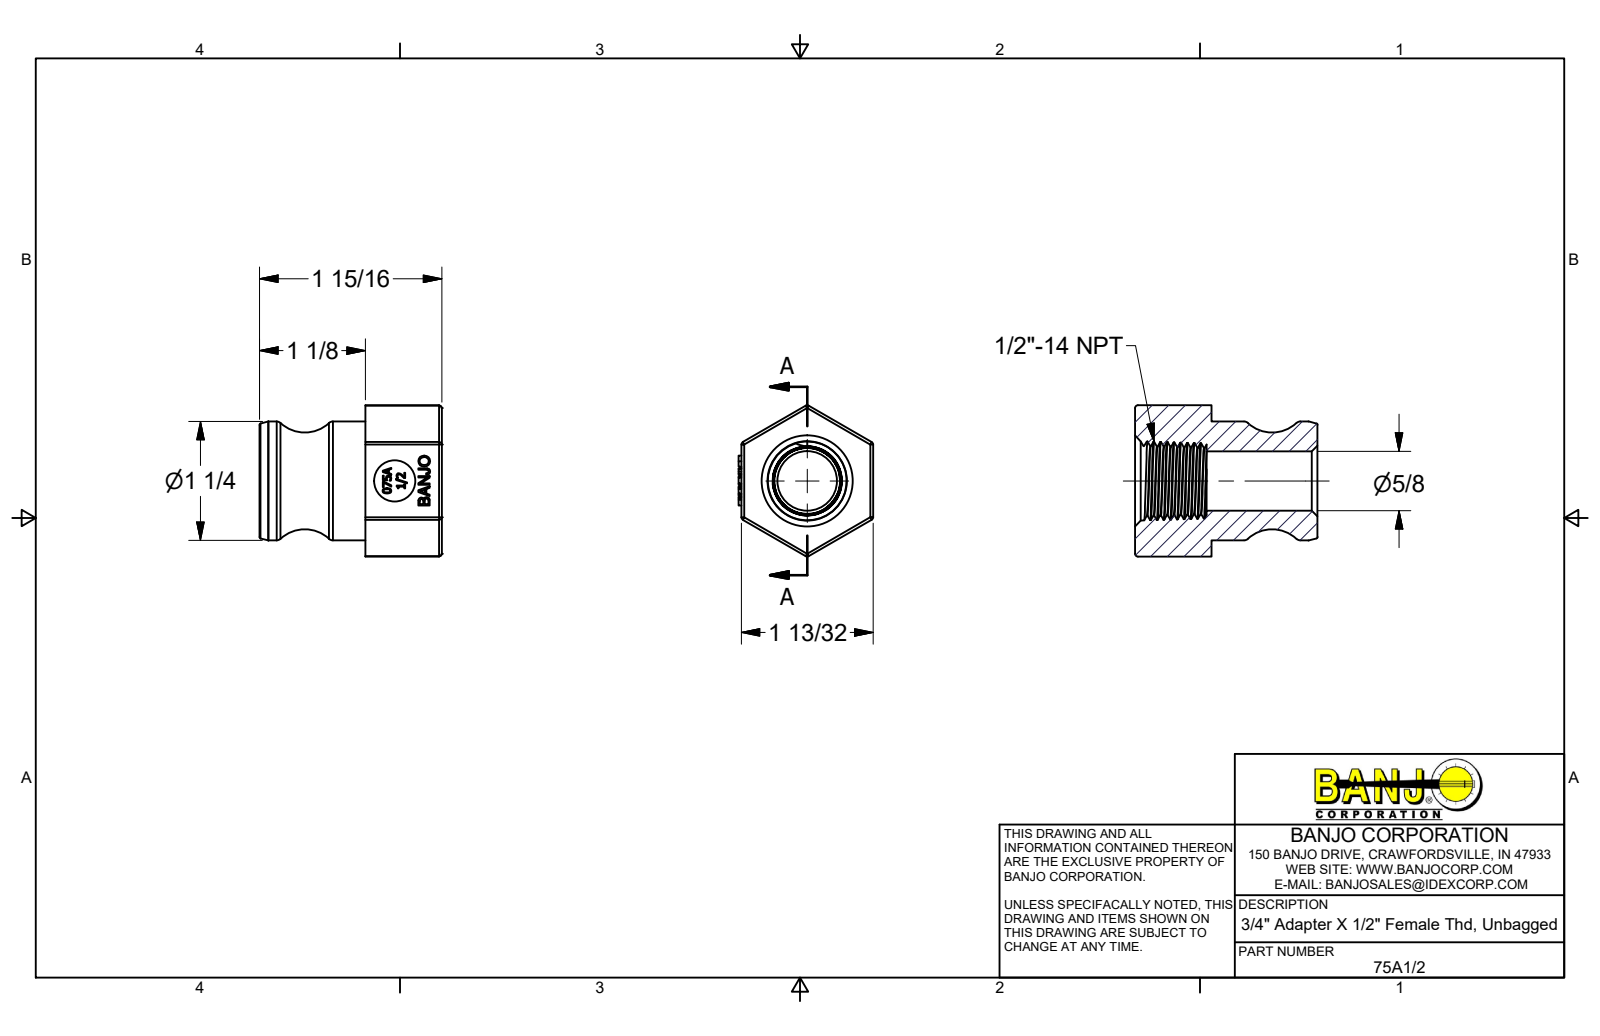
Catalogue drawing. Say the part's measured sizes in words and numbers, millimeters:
The part is named "75A050; 75A050U". Its 3-D file was written by "Autodesk Inventor 2017 (AUTOMOTIVE_DESIGN)". It is 1 solid with 214 faces: 110 planar, 17 cylindrical and 87 other. Overall it measures 49.21 by 40.82 by 36.32 millimeters. Its volume is 30 856 cubic millimeters and its surface area 10 537 square millimeters. Round holes: 1 of diameter 11.11, 1 of diameter 16. Round bosses or shafts: 1 of diameter 32.11. Partial cylindrical surfaces (rounded edges, fillets, slot ends): 6 of radius 0.76, 6 of radius 0.79, 1 of radius 6.62. The main face-to-face distances are 35.56, 49.22, 35.55, 28.58, 20.64, 35.3, 29.91, 1.33, 19.31, 1.02.
